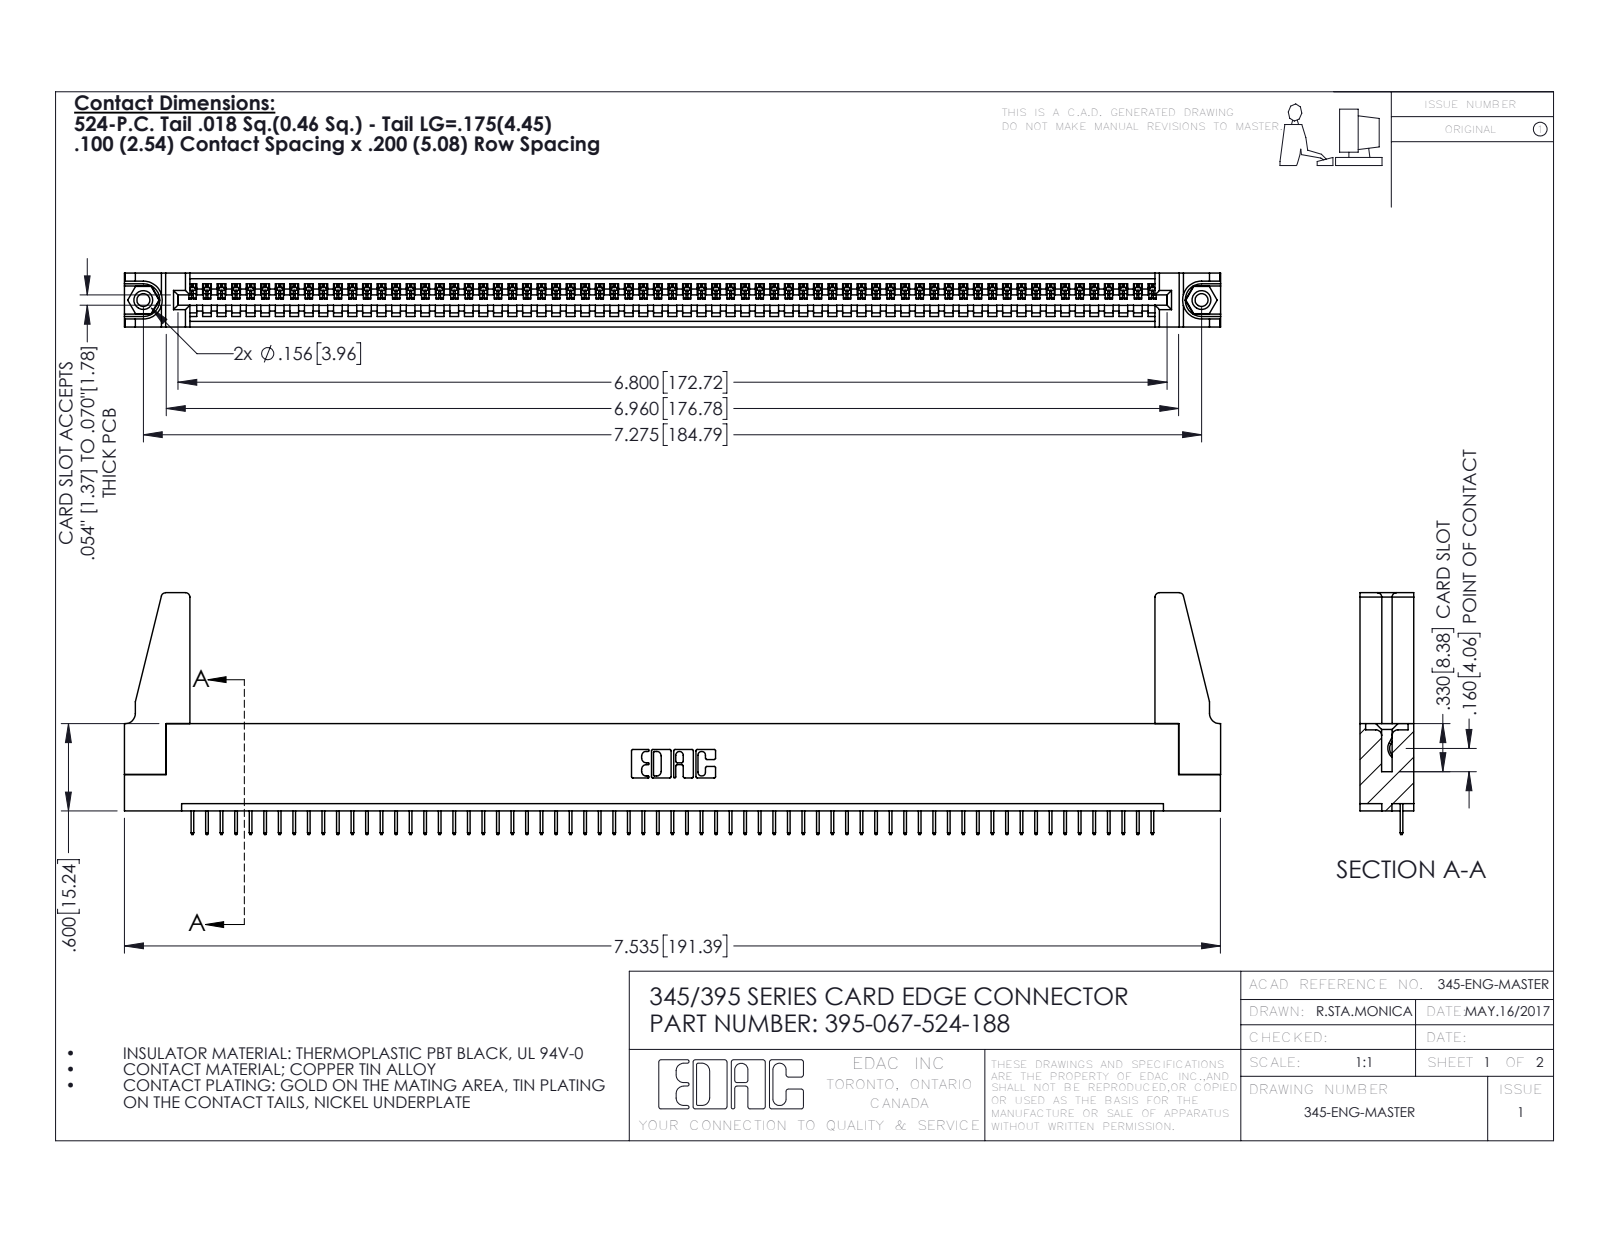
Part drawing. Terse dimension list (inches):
name: 395-067-524-188; 345-292-001_345-293-124; 345-250-001_345-250-001-102; 345-220-078_345-220-088 (+1 more)
written by: SolidWorks 2016 (CONFIG_CONTROL_DESIGN)
unit: in
bodies: 72 solids, 4404 faces (3234 planar, 1154 cylindrical, 16 other)
size: 7.536 × 1.662 × 0.37
volume: 1.304 in³; area: 41.39 in²
holes: 2× ⌀0.089, 2× ⌀0.125, 2× ⌀0.156, 1× ⌀0.064
bosses: 2× ⌀0.155
rounds: 134× R0.006, 22× R0.01, 8× R0.03, 6× R0.007, 6× R0.031, 3× R0.026, 2× R0.031, 2× R0.04
face distances: 0.072, 0.298, 0.37, 0.2, 0.098, 0.272, 0.025, 0.225, 0.072, 0.149
hole spacings: 0.27, 7.039, 7.275
